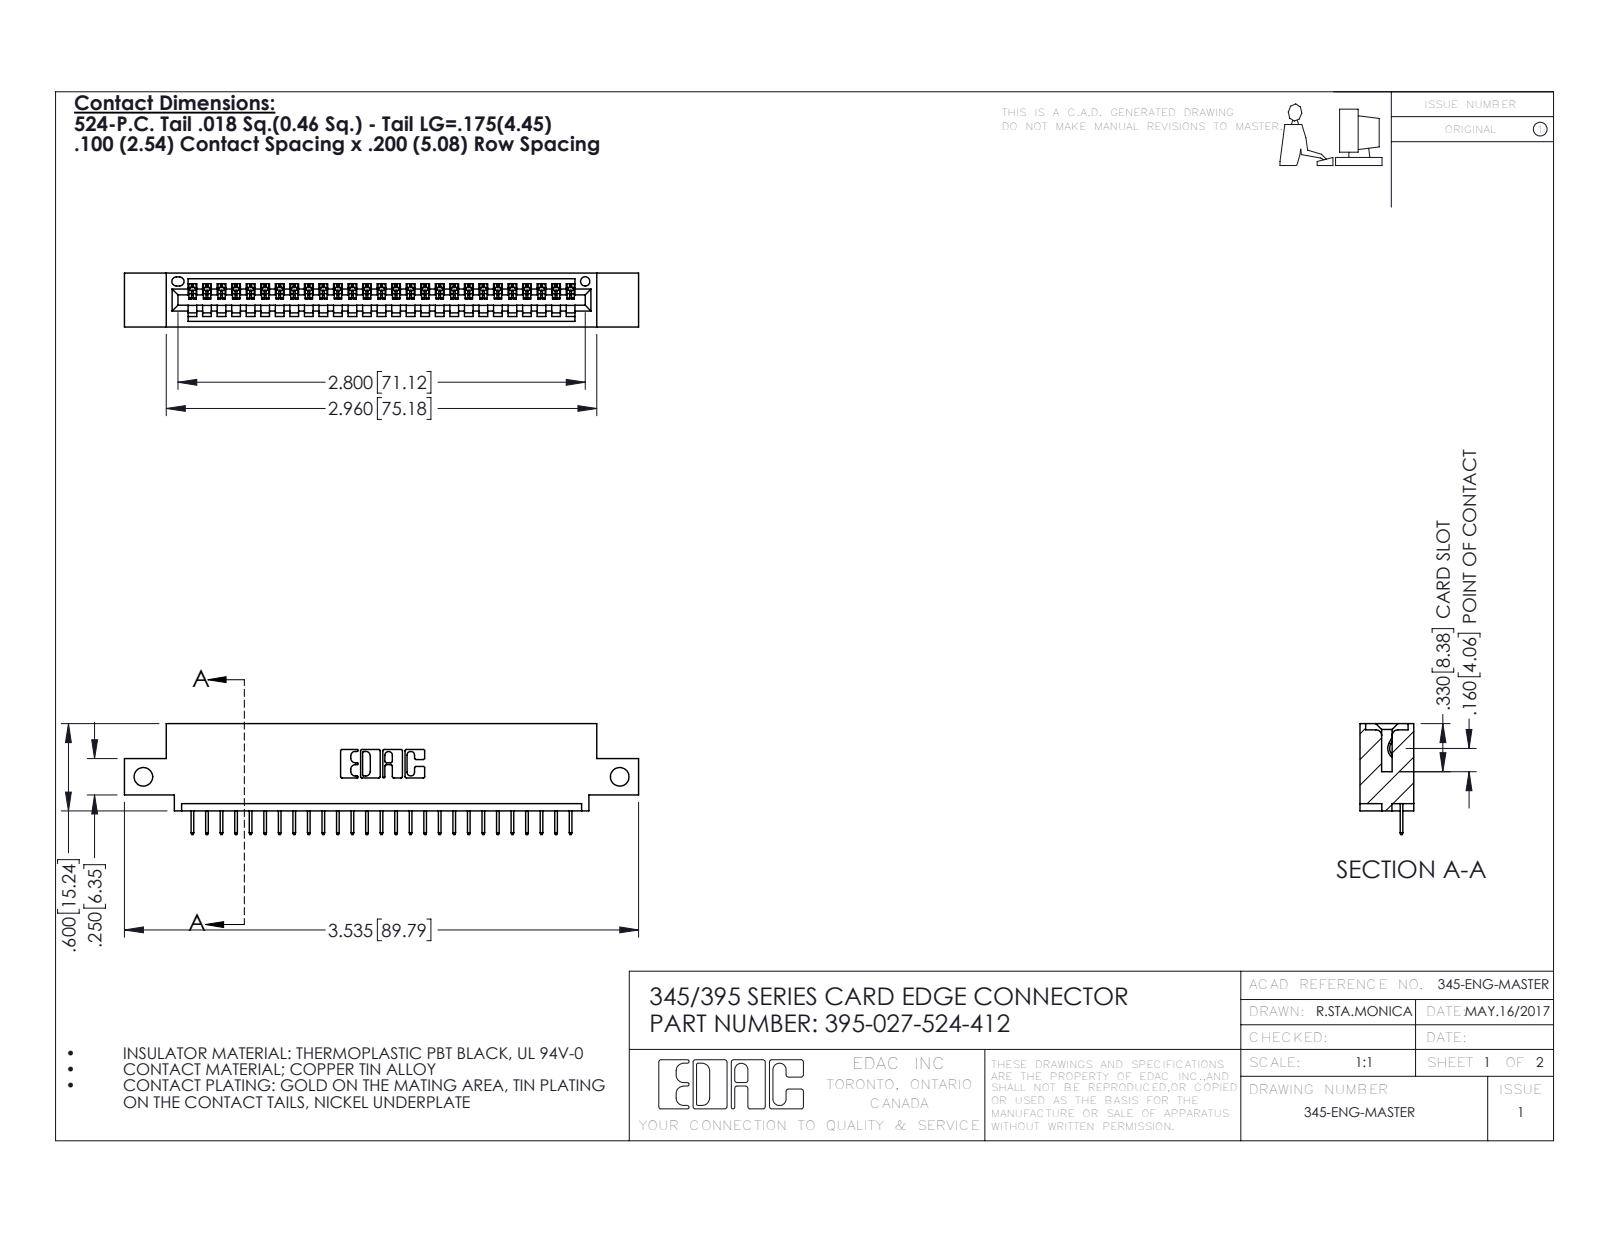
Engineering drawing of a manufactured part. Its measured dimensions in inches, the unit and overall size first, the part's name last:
Units: inches
Overall size (bounding box): 3.535 × 0.762 × 0.37
Round holes (diameter × count): ⌀0.128 ×2, ⌀0.064 ×1
Partial cylindrical surfaces — rounded edges, fillets, slot ends (radius × count): R0.006 ×54, R0.01 ×22, R0.007 ×6, R0.031 ×6, R0.026 ×3, R0.031 ×2, R0.04 ×2, R0.014 ×1
Main face-to-face distances: 0.072, 0.298, 0.37, 0.2, 0.098, 0.272, 0.025, 0.225, 0.072, 0.149
Hole centre spacings: 3.275
Volume: 0.497 in³ · Surface area: 15.83 in²
Bodies: 28 solids, 1804 faces (1326 planar, 478 cylindrical, 0 other)
Part name (STEP PRODUCT): 395-027-524-412; 345 Part_0.110 Offset - Side Mount; 345-292-001_345-293-124
STEP written by: SolidWorks 2016 (CONFIG_CONTROL_DESIGN)
